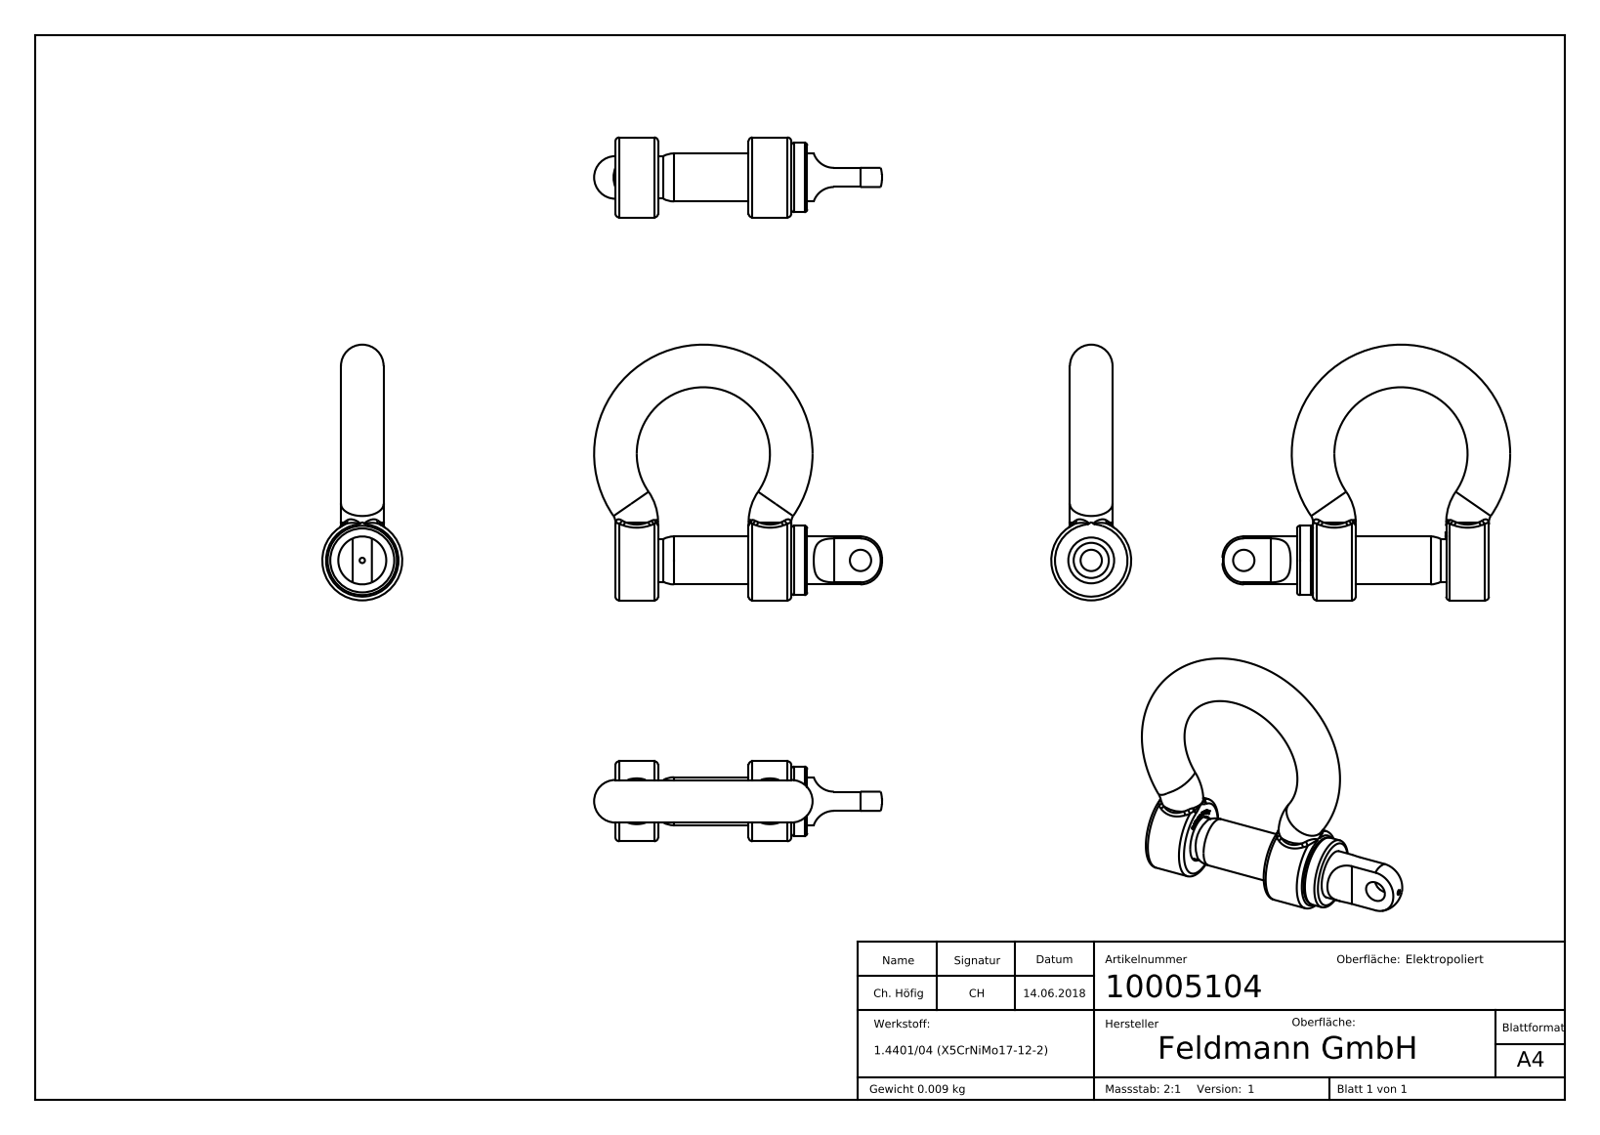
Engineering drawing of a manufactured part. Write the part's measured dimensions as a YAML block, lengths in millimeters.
part_name: "1000510X Teil1_10005104 Teil1; 10005104; 1000510X Teil2_10005104 Teil2"
step_written_by: "SolidWorks 2015 (CONFIG_CONTROL_DESIGN)"
units: millimeters
bodies: {solids: 2, faces: 311, planar: 119, cylindrical: 28, other: 164}
overall_size: [27, 24, 7.5]
volume: 1087
surface_area: 1249
round_holes:
  - {diameter: 2, count: 1}
  - {diameter: 3.3, count: 1}
round_bosses_or_shafts:
  - {diameter: 7.5, count: 1}
  - {diameter: 6.5, count: 1}
  - {diameter: 4.5, count: 1}
  - {diameter: 4, count: 1}
partial_cylinders:
  - {radius: 2, count: 4}
face_to_face_distances: [12.5, 4, 16.5, 8.5, 1.8, 18, 14, 5.5, 1.5, 0.5]
